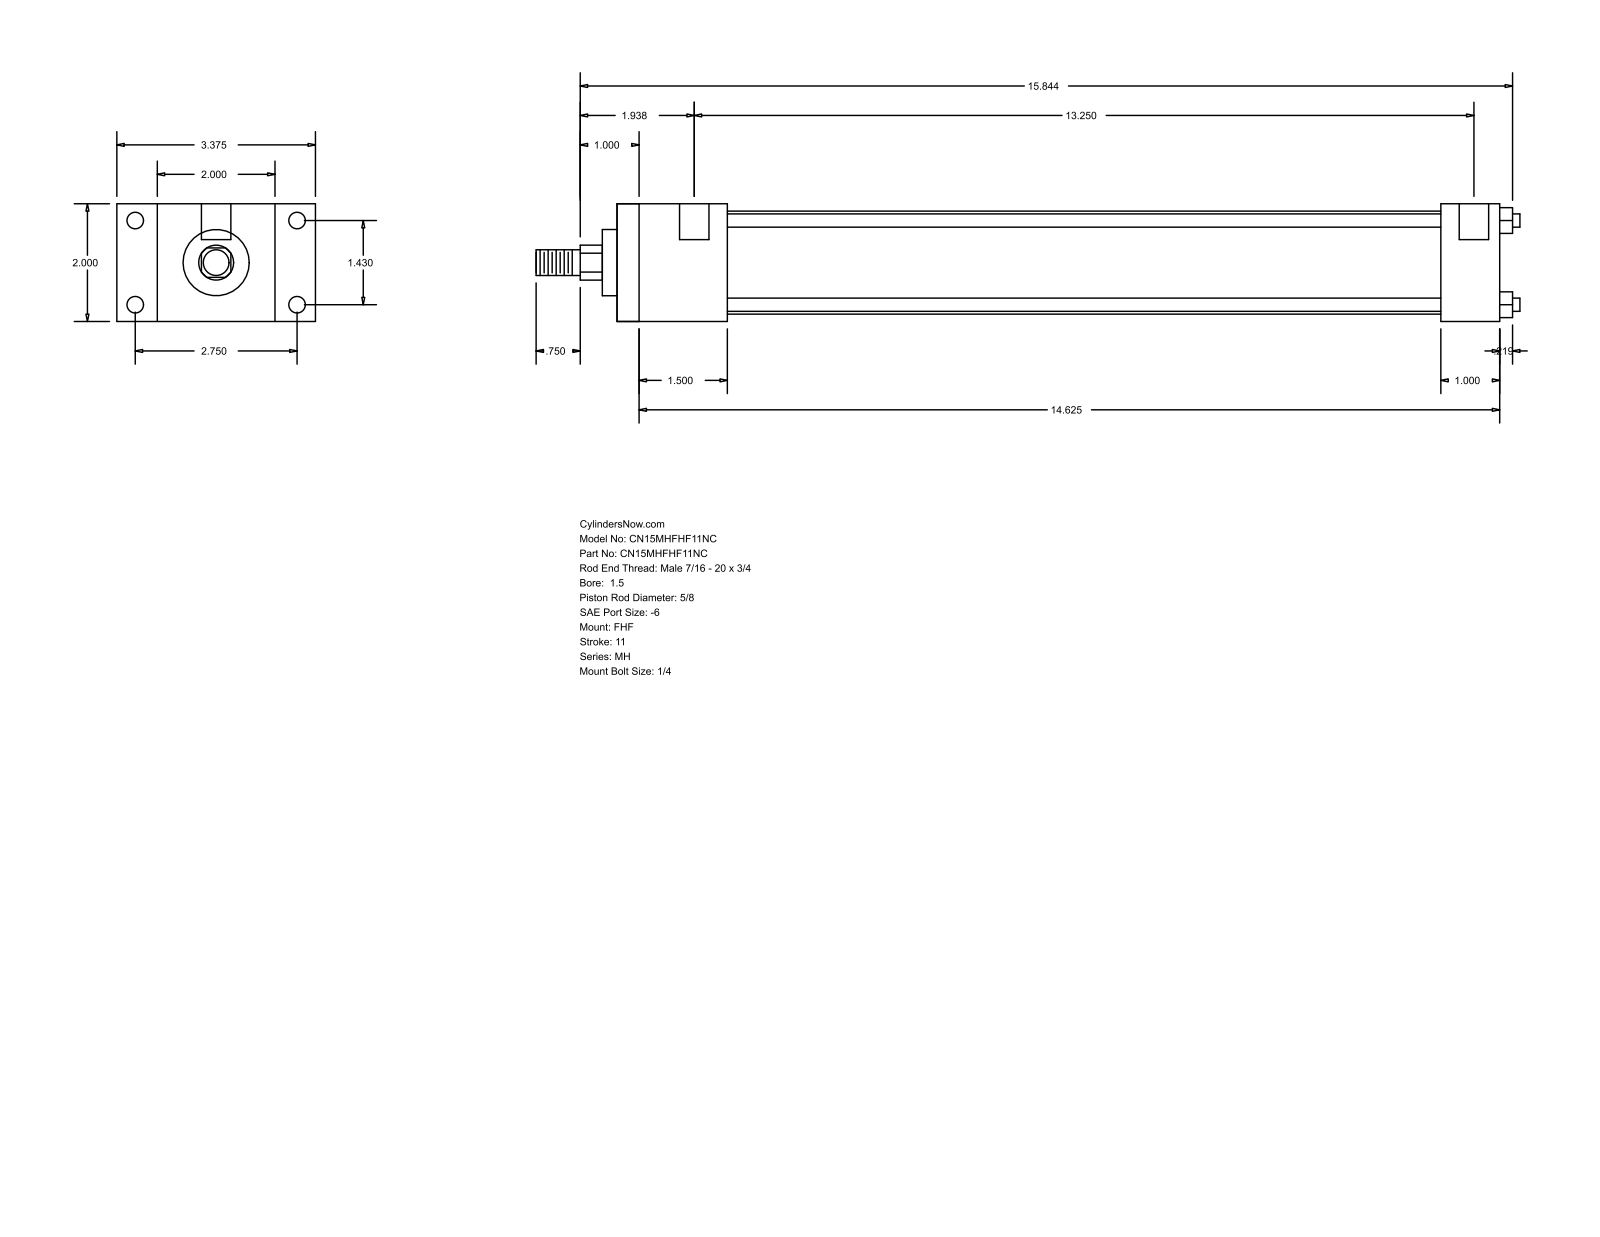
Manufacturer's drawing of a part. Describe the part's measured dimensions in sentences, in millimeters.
The part is named "MH_FHF__0150_0.625". Its 3-D file was written by "GSSL Pune (CONFIG_CONTROL_DESIGN)". It is 0 solids with 88 faces: 60 planar, 28 cylindrical and 0 other. Overall it measures 424.66 by 85.72 by 50.8 millimeters. Round holes: 4 of diameter 5.56, 4 of diameter 7.14, 2 of diameter 12.7. Round bosses or shafts: 4 of diameter 5.71, 1 of diameter 44.45, 1 of diameter 28.57, 1 of diameter 15.88, 1 of diameter 11.11. Partial cylindrical surfaces (rounded edges, fillets, slot ends): 1 of radius 7.54. The main face-to-face distances are 50.8, 17.46, 68.26, 47.62, 85.72, 381, 333.38, 25.4, 355.6, 307.98. The hole center spacings are 36.32, 69.84, 78.72, 339.72, 3.17, 336.55.
